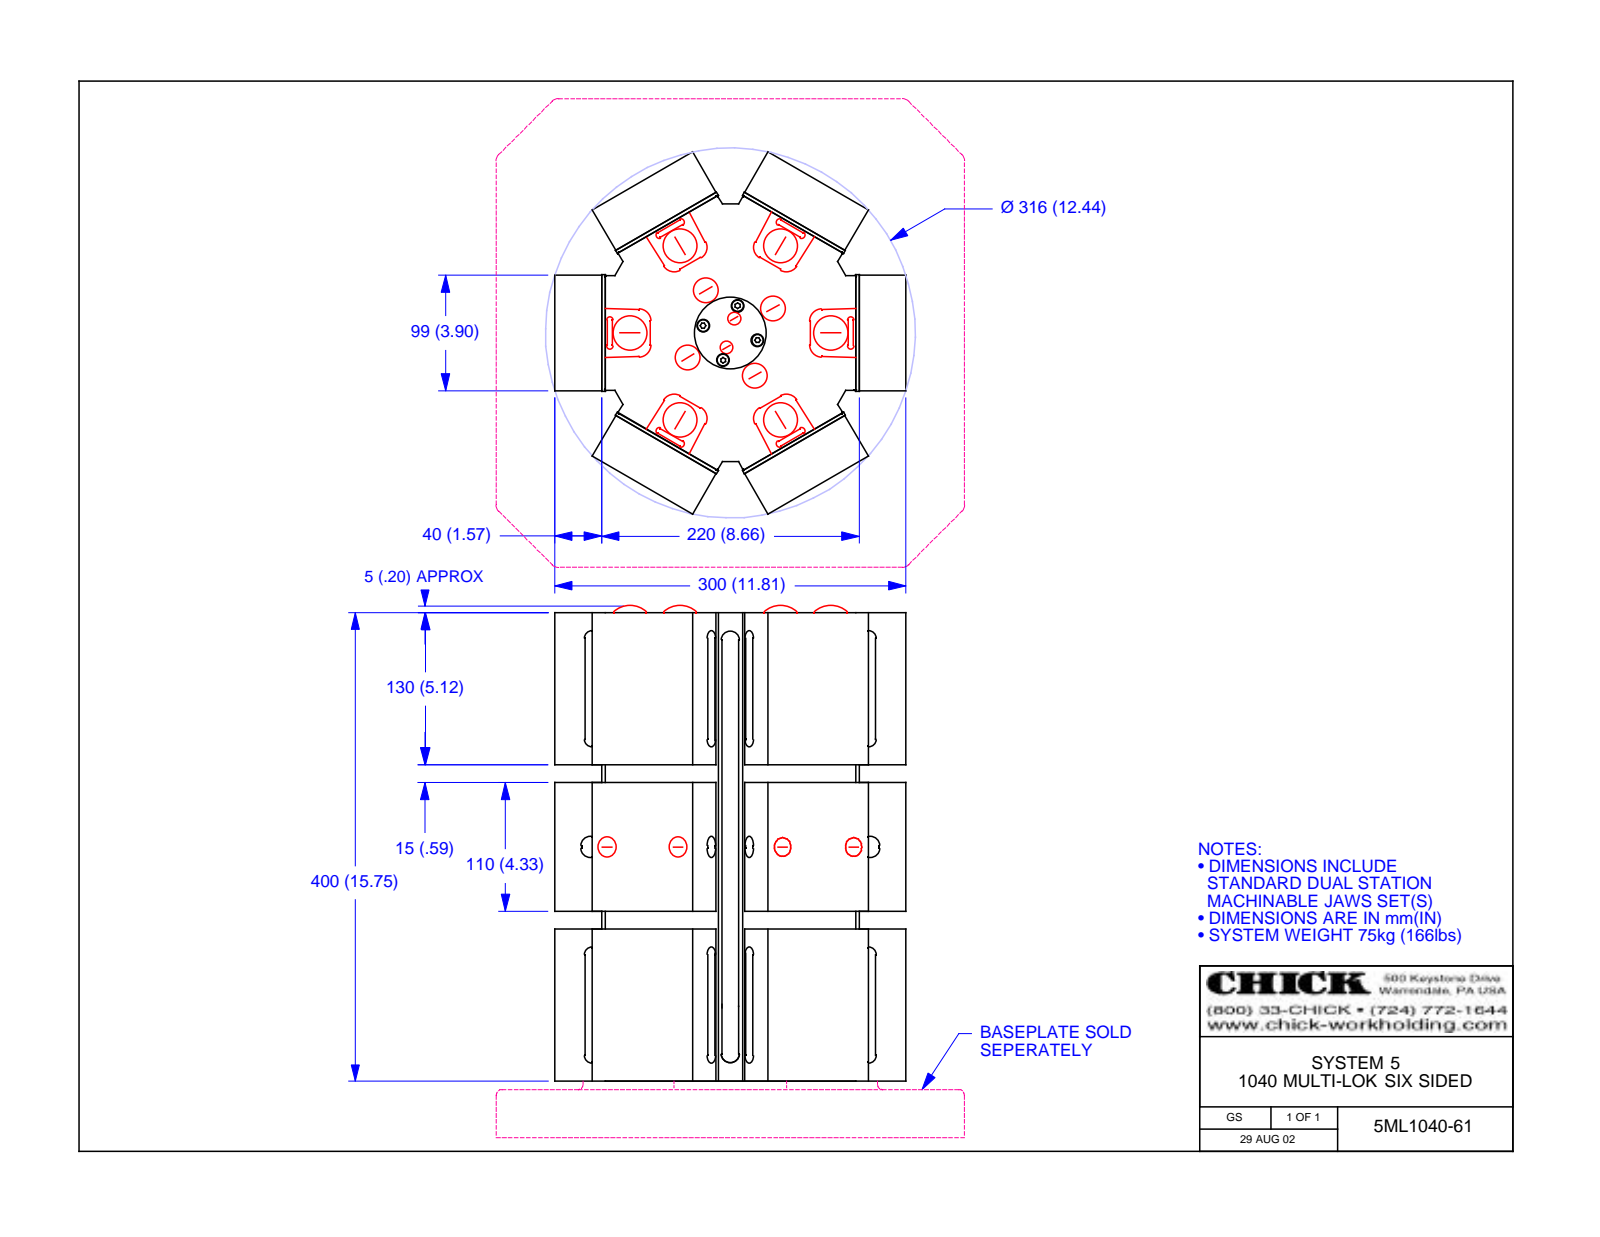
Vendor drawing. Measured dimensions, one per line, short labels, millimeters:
name: 5ML1040-61; 5CLM1040-61; 5DS1040-10-40; 5FJ1040-10-40 (+2 more)
written by: Autodesk Inventor 2013 (AUTOMOTIVE_DESIGN)
unit: mm
bodies: 25 solids, 3289 faces (1561 planar, 606 cylindrical, 1122 other)
size: 405.5 × 307.69 × 299.4
volume: 21 580 000 mm³; area: 1 957 000 mm²
holes: 30× ⌀14.15, 30× ⌀19.34, 20× ⌀12.7, 18× ⌀6.65, 18× ⌀9, 12× ⌀8.65, 10× ⌀8.4, 10× ⌀14, 10× ⌀16, 6× ⌀10.11, 4× ⌀4.92, 4× ⌀13.5
bosses: 12× ⌀8.4, 4× ⌀14
rounds: 156× R1.5, 40× R4.8, 24× R11.1, 20× R3, 6× R7
face distances: 3, 217, 39.7, 42.7, 256.7, 259.7, 220, 214, 37.49, 61.51
hole spacings: 150, 165.53, 70, 185, 197.8, 300, 308.06, 35
